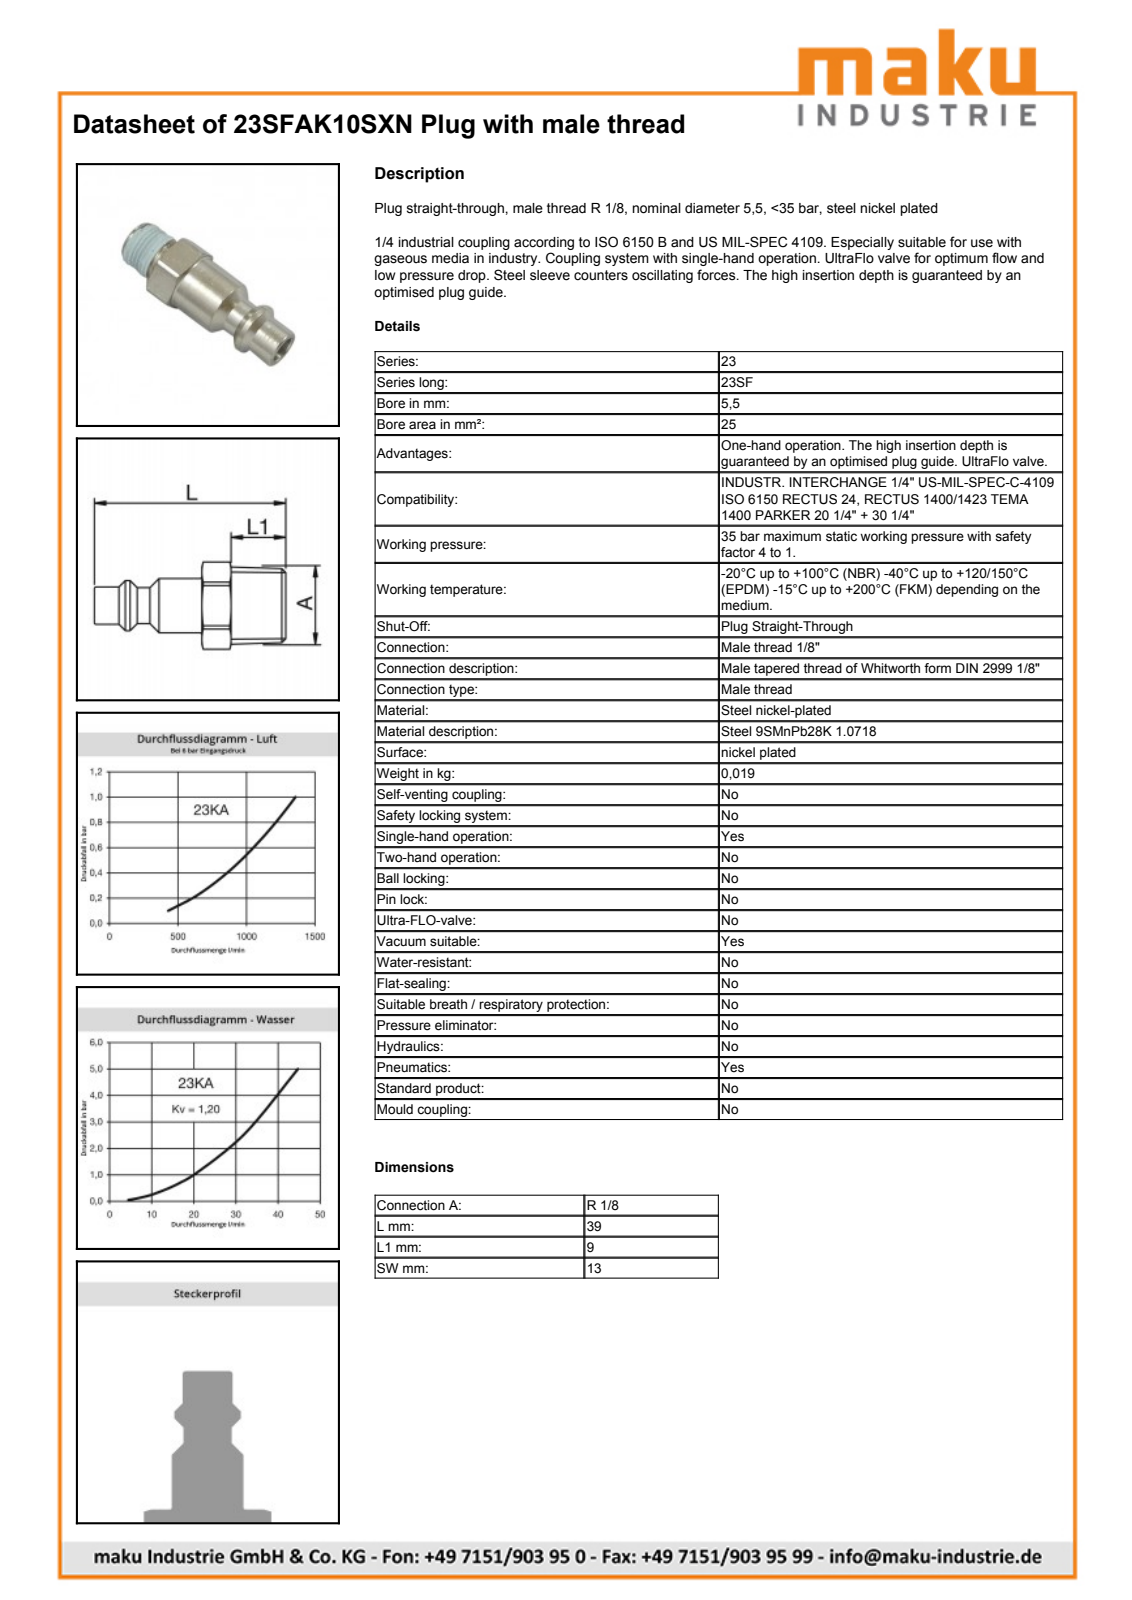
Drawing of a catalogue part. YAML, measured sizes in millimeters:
part_name: "D108568"
step_written_by: "Autodesk Inventor 2013 (AUTOMOTIVE_DESIGN)"
units: millimeters
bodies: {solids: 1, faces: 41, planar: 10, cylindrical: 11, other: 20}
overall_size: [39, 14.65, 13]
volume: 2419
surface_area: 2147
round_holes:
  - {diameter: 5.5, count: 1}
round_bosses_or_shafts:
  - {diameter: 11.8, count: 1}
  - {diameter: 10.9, count: 1}
  - {diameter: 8.1, count: 1}
  - {diameter: 7.8, count: 1}
partial_cylinders:
  - {radius: 7.33, count: 1}
face_to_face_distances: [13, 30, 23.6, 6.4, 39, 15.4, 9]
